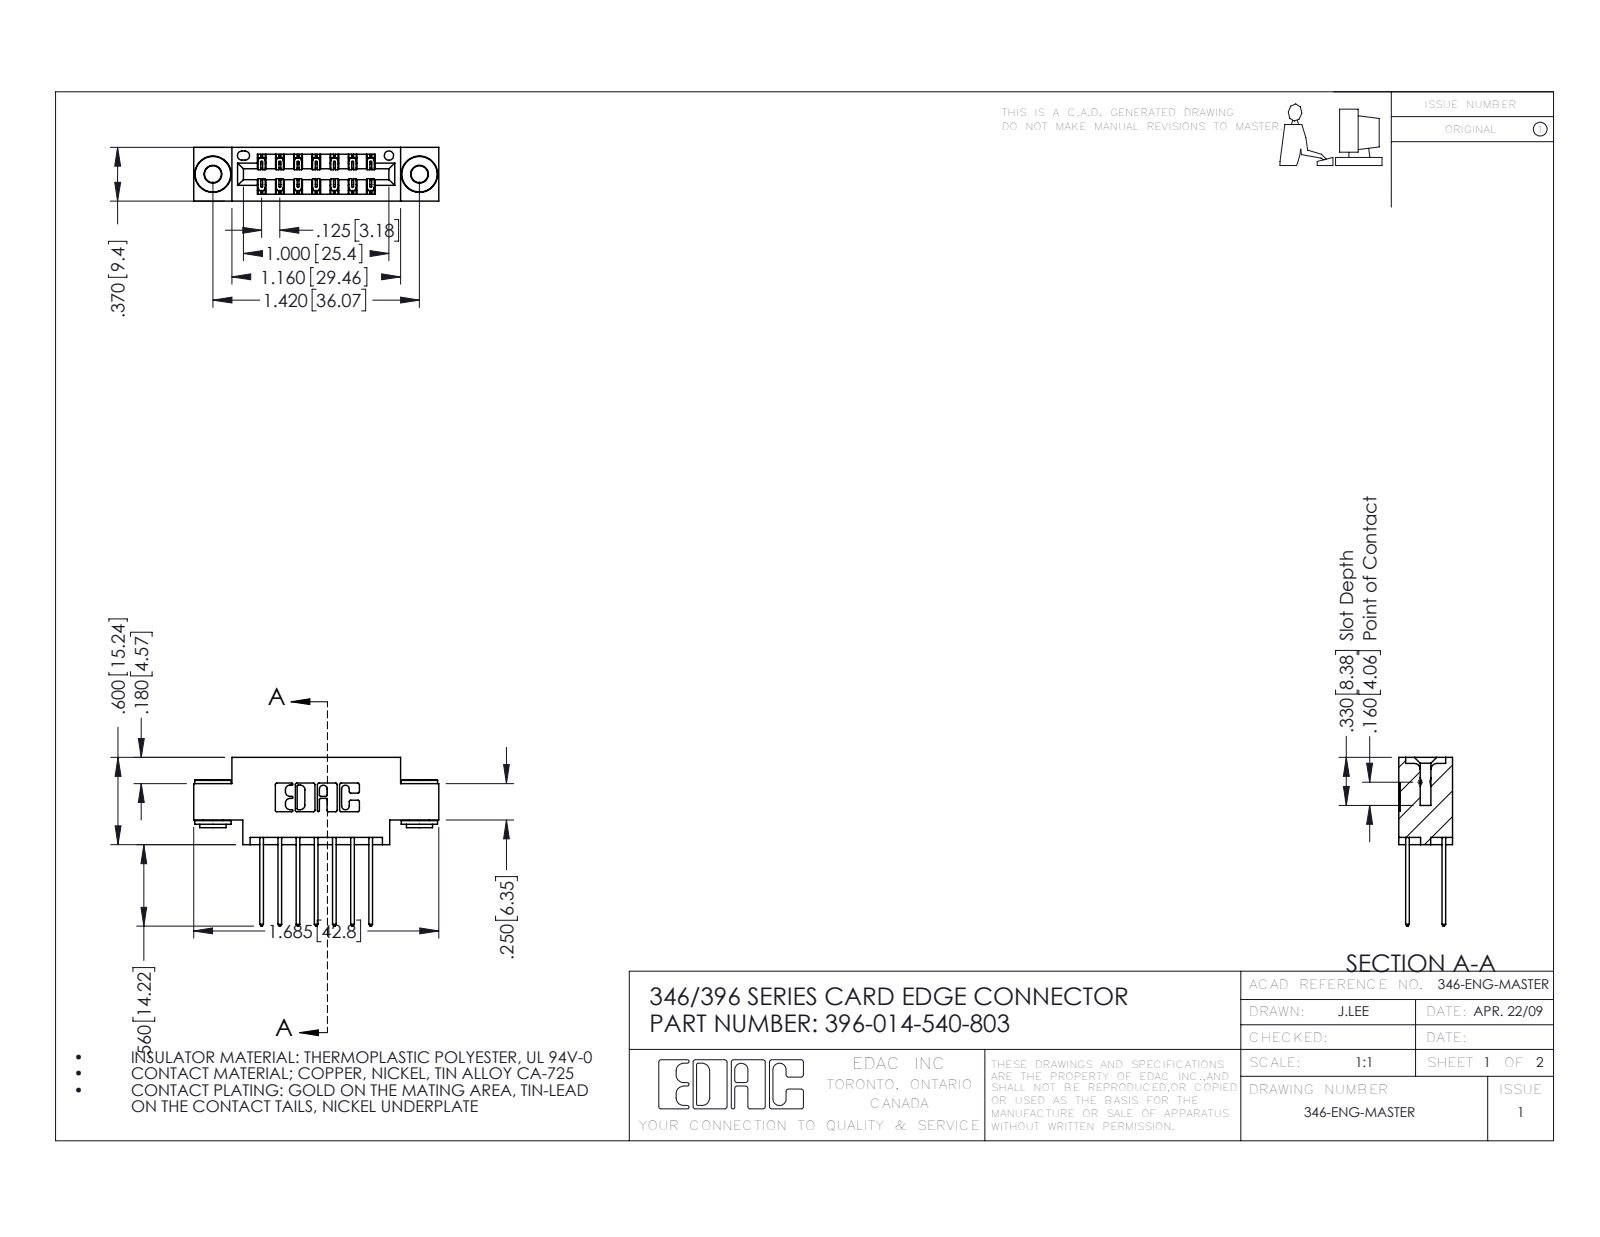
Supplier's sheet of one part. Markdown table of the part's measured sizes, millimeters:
| quantity | value |
| --- | --- |
| part name | 396-014-540-803; 345-292-001_345-293-140; 345-250-002_345-250-002-102; 346 Part_0.170 Offset - 0.156 Dia-TH |
| STEP written by | SolidWorks 2016 (CONFIG_CONTROL_DESIGN) |
| units | millimeters |
| bodies | 17 solids, 892 faces (580 planar, 304 cylindrical, 8 other) |
| overall size | 42.8 × 29.5 × 9.4 |
| volume | 3 820 mm³ |
| surface area | 5 345 mm² |
| round holes (diameter × count) | 2.9 × 2, 4 × 2, 1.6 × 1 |
| round bosses / shafts (diameter × count) | 6.4 × 2, 4.6 × 2, 3.5 × 2 |
| partial cylindrical surfaces (radius × count) | 0.3 × 22, 0.2 × 21, 0.3 × 14, 0.2 × 6, 0.8 × 6, 0.7 × 3, 0.4 × 2, 0.6 × 2 |
| main face-to-face distances | 6.4, 9.4, 1.2, 8.2, 0.6, 1.8, 7.6, 7, 5.7, 3.8 |
| hole center spacings | 6.2, 30.9, 36.1 |
